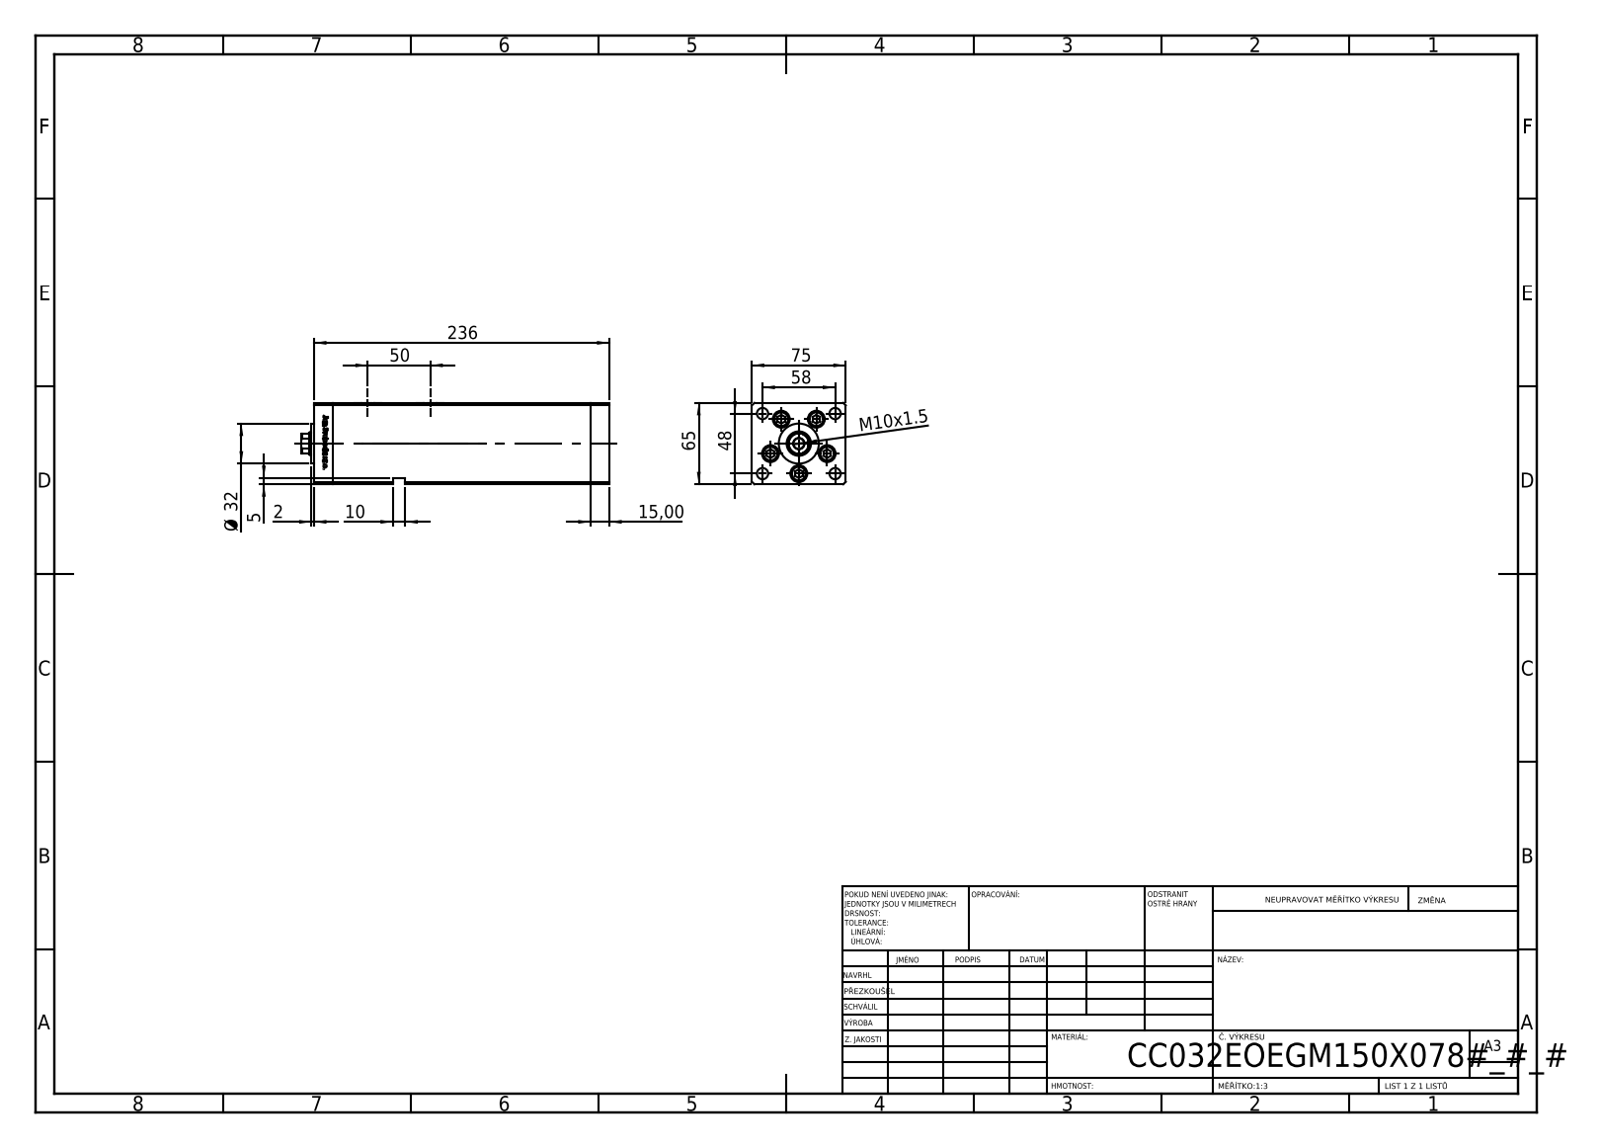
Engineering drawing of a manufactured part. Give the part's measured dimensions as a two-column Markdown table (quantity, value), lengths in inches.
| quantity | value |
| --- | --- |
| part name | V220C_FRONT_E; V220C BACK_E; ALLEN BOLT; V220C_E MIDDLE (+1 more) |
| STEP written by | SolidWorks 2019 (CONFIG_CONTROL_DESIGN) |
| units | inches |
| bodies | 14 solids, 1212 faces (473 planar, 165 cylindrical, 574 other) |
| overall size | 9.685 × 2.953 × 2.559 |
| volume | 59.55 in³ |
| surface area | 262.7 in² |
| round holes (diameter × count) | 0.354 × 9, 0.531 × 5, 0.413 × 4, 0.65 × 4, 0.079 × 2, 0.518 × 2, 0.335 × 1, 0.709 × 1, 0.768 × 1 |
| round bosses / shafts (diameter × count) | 0.492 × 5, 0.315 × 5, 1.26 × 1 |
| partial cylindrical surfaces (radius × count) | 0.037 × 2, 0.335 × 1 |
| main face-to-face distances | 2.953, 2.559, 0.591, 8.11, 8.701, 9.291, 2.146, 0.413, 1.033, 1.919 |
| hole center spacings | 0.945, 1.482, 2.283, 0.617, 0.678, 1.091, 1.135, 1.142 |
